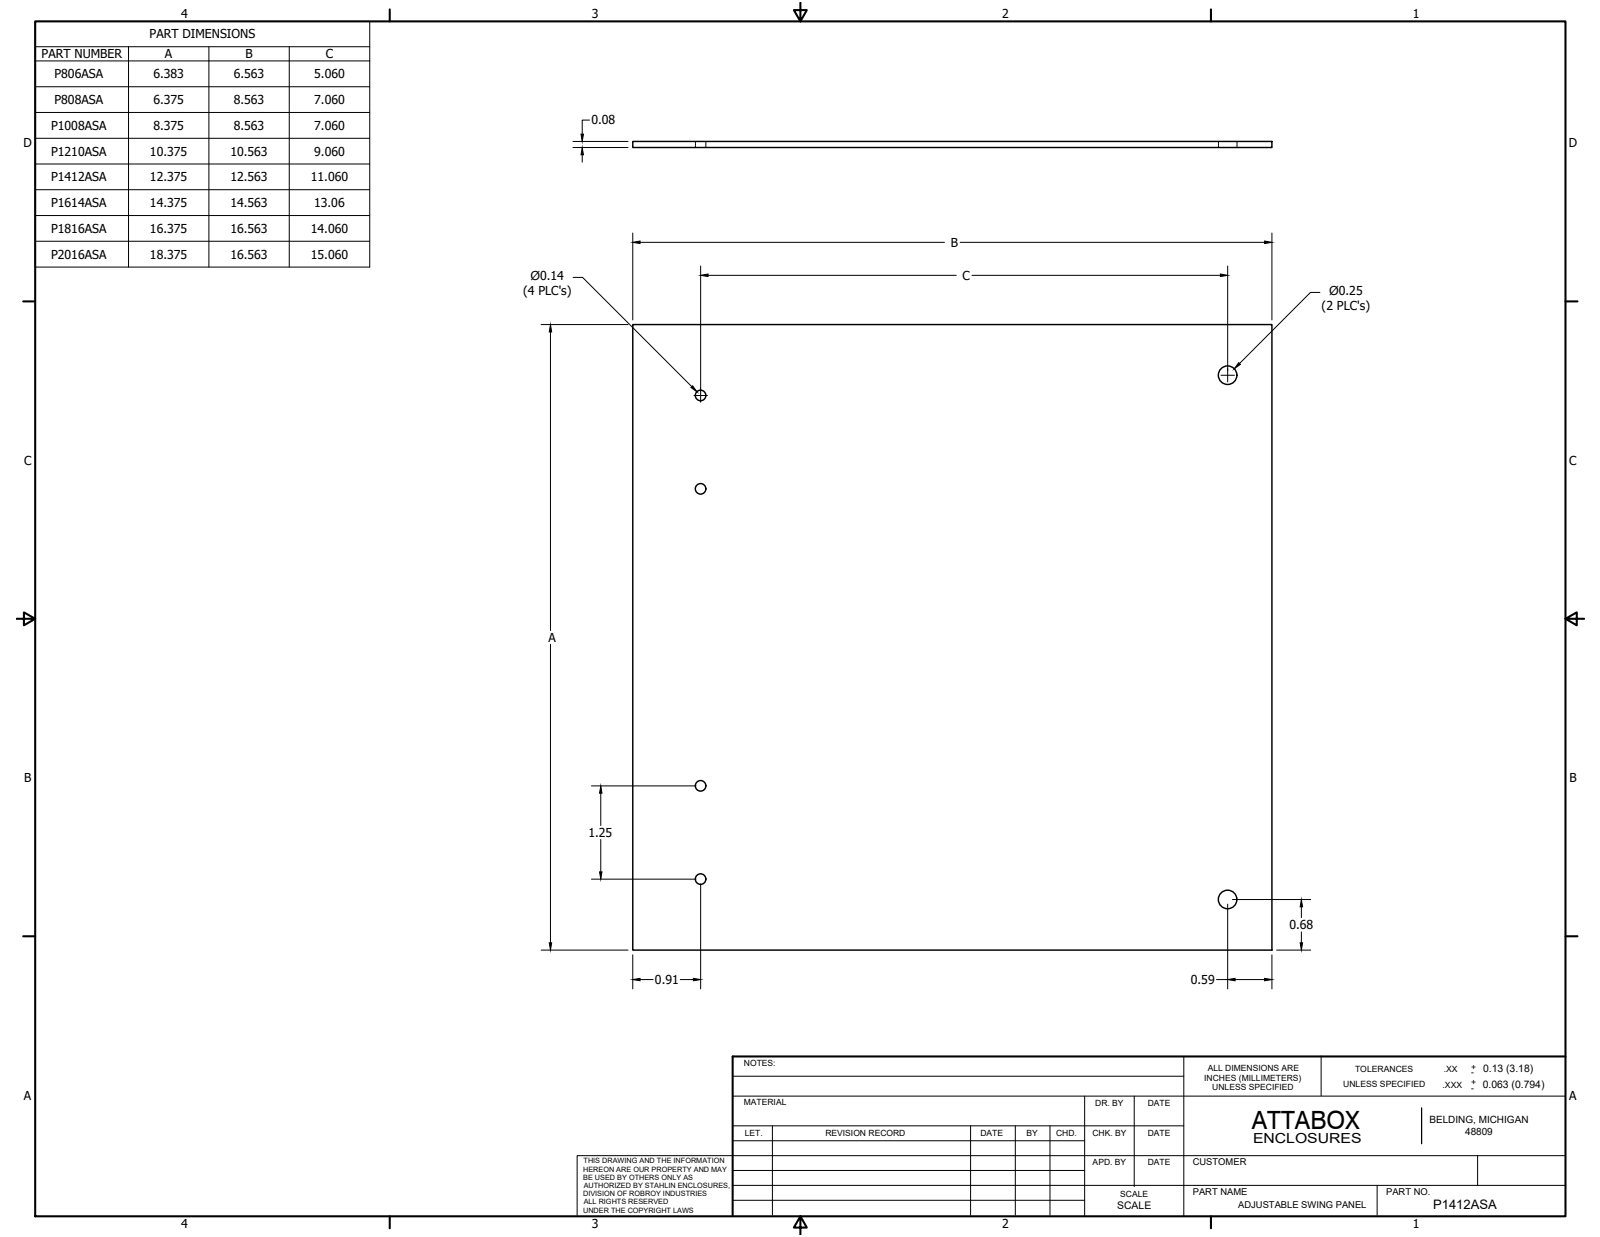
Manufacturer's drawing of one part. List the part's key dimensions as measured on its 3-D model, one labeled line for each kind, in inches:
Part name (STEP PRODUCT): P1412ASAL
STEP written by: Autodesk Inventor 11 (AUTOMOTIVE_DESIGN)
Units: inches
Bodies: 1 solid, 12 faces (6 planar, 6 cylindrical, 0 other)
Overall size (bounding box): 12.563 × 12.375 × 0.08
Volume: 12.42 in³ · Surface area: 314.9 in²
Round holes (diameter × count): ⌀0.14 ×4, ⌀0.25 ×2
Main face-to-face distances: 0.08, 12.375, 12.562
Hole centre spacings: 1.25, 9.226, 11.063, 11.165, 14.578, 15.422, 7.976, 10.476
